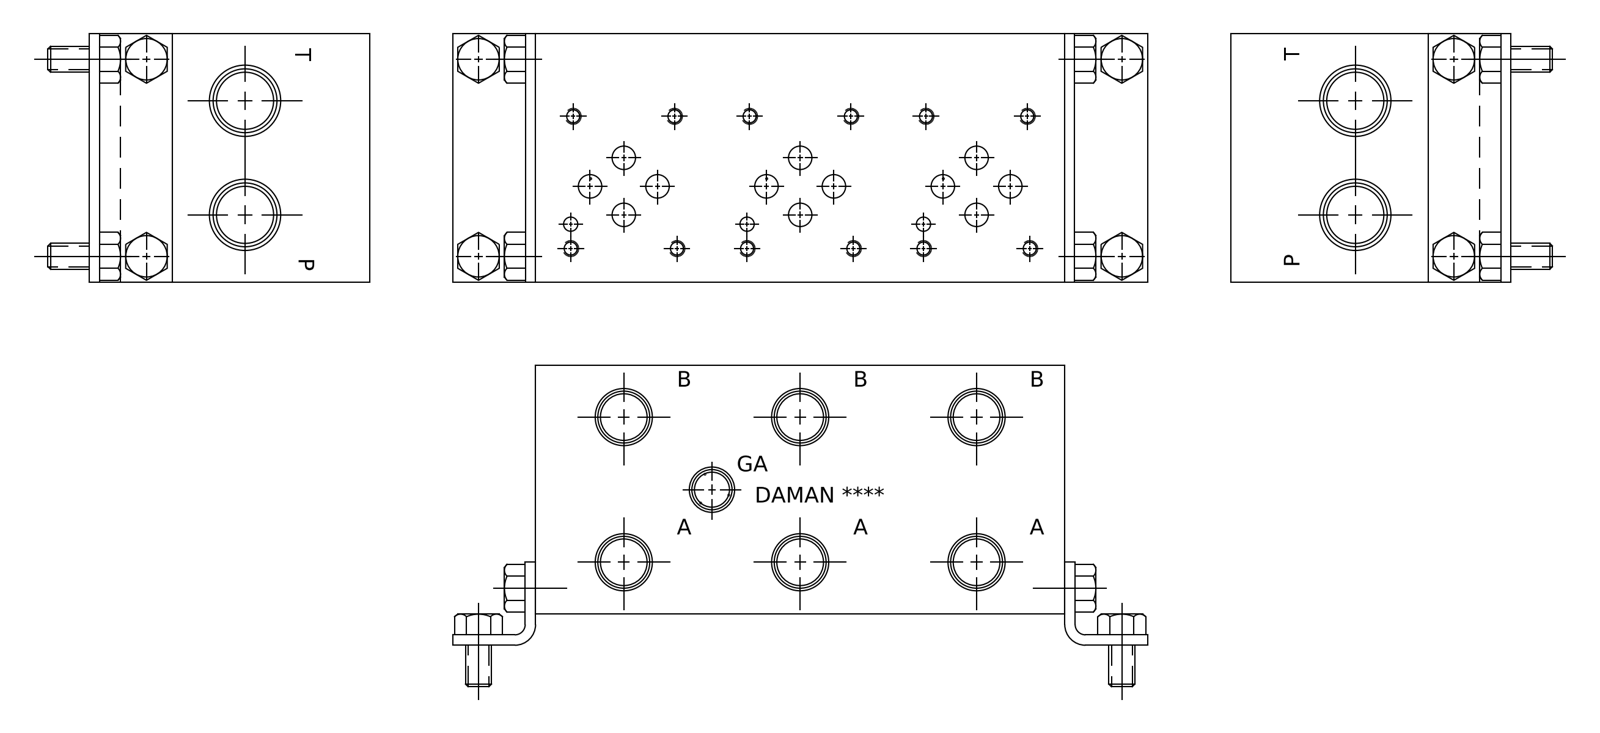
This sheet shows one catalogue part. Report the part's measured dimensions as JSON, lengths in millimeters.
{"part_name": "Part_AD03P032P_3D", "step_written_by": "Autodesk Inventor 2020 (AUTOMOTIVE_DESIGN)", "units": "millimeters", "bodies": {"solids": 1, "faces": 642, "planar": 360, "cylindrical": 73, "other": 209}, "overall_size": [161.93, 76.2, 76.2], "volume_mm3": 872538, "surface_area_mm2": 79425, "round_holes": [[4.22, 12], [5, 12], [7.14, 9], [14.3, 6], [17.3, 6], [3.96, 3], [6.35, 3], [6.76, 2], [8, 2], [15.88, 2], [17.48, 2], [21.59, 2]], "face_to_face_distances": [76.2, 161.93, 15.37, 146.56, 11.73, 64.47, 131.19, 11.69, 76.16, 60.2], "hole_center_spacings": [53.97, 53.98, 107.95, 19.95, 22.05, 33.55, 40.49, 51.45]}
